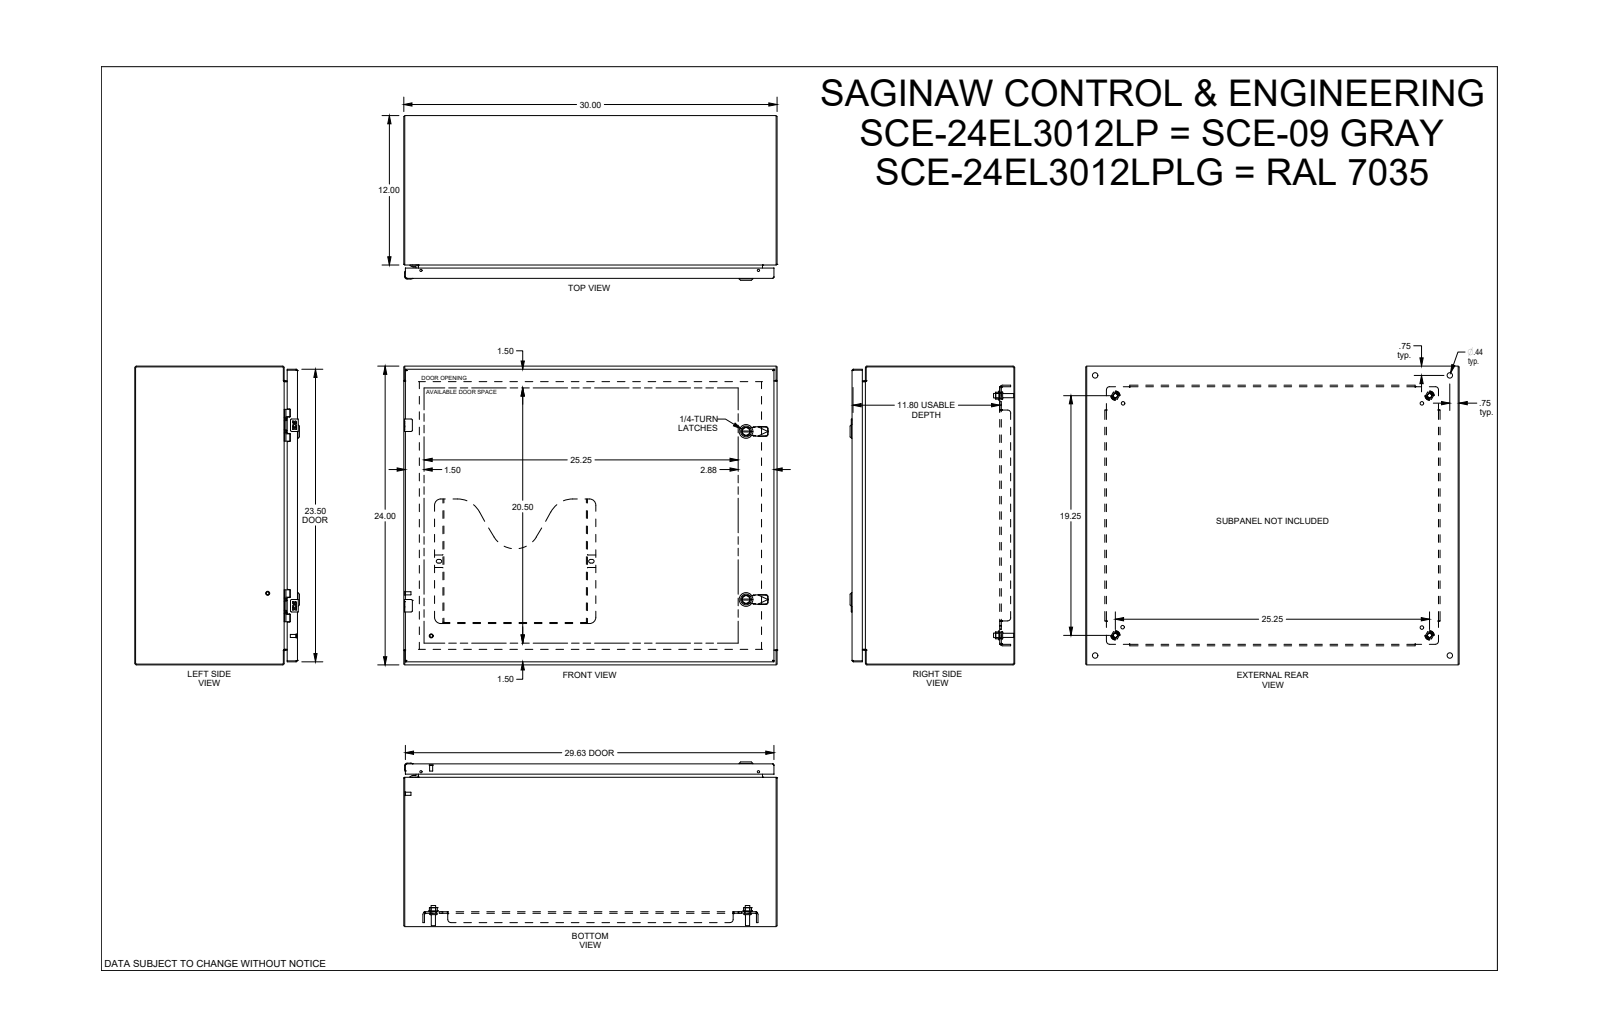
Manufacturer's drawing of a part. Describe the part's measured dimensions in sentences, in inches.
The part is named "SCE-24EL3012LP". Its 3-D file was written by "SolidWorks 2021 (AUTOMOTIVE_DESIGN)". It is 47 solids with 2843 faces: 1115 planar, 858 cylindrical and 870 other. Overall it measures 30 by 24 by 13.23 inches. Its volume is 319.3 cubic inches and its surface area 7 750 square inches. Round holes: 4 of diameter 0.172, 4 of diameter 0.205, 4 of diameter 0.244, 4 of diameter 0.266, 4 of diameter 0.281, 4 of diameter 0.367, 4 of diameter 0.375, 4 of diameter 0.437, 4 of diameter 0.5, 2 of diameter 0.04, 2 of diameter 0.188, 2 of diameter 0.197. Round bosses or shafts: 6 of diameter 0.17, 4 of diameter 0.366, 4 of diameter 0.332, 4 of diameter 0.25, 4 of diameter 0.248, 4 of diameter 0.24, 3 of diameter 0.196, 2 of diameter 1.102. Partial cylindrical surfaces (rounded edges, fillets, slot ends): 56 of radius 0.012, 28 of radius 0.01, 24 of radius 0.015, 20 of radius 0.02, 17 of radius 0.04, 13 of radius 0.06, 12 of radius 0.029, 12 of radius 0.1. The main face-to-face distances are 0.075, 0.06, 12.998, 0.075, 13.073, 13.013, 12.938, 1.2, 11.873, 1.125. The hole center spacings are 14.5, 0.02, 0.493, 0.985, 0.875, 3.173, 4.493, 20.38.
